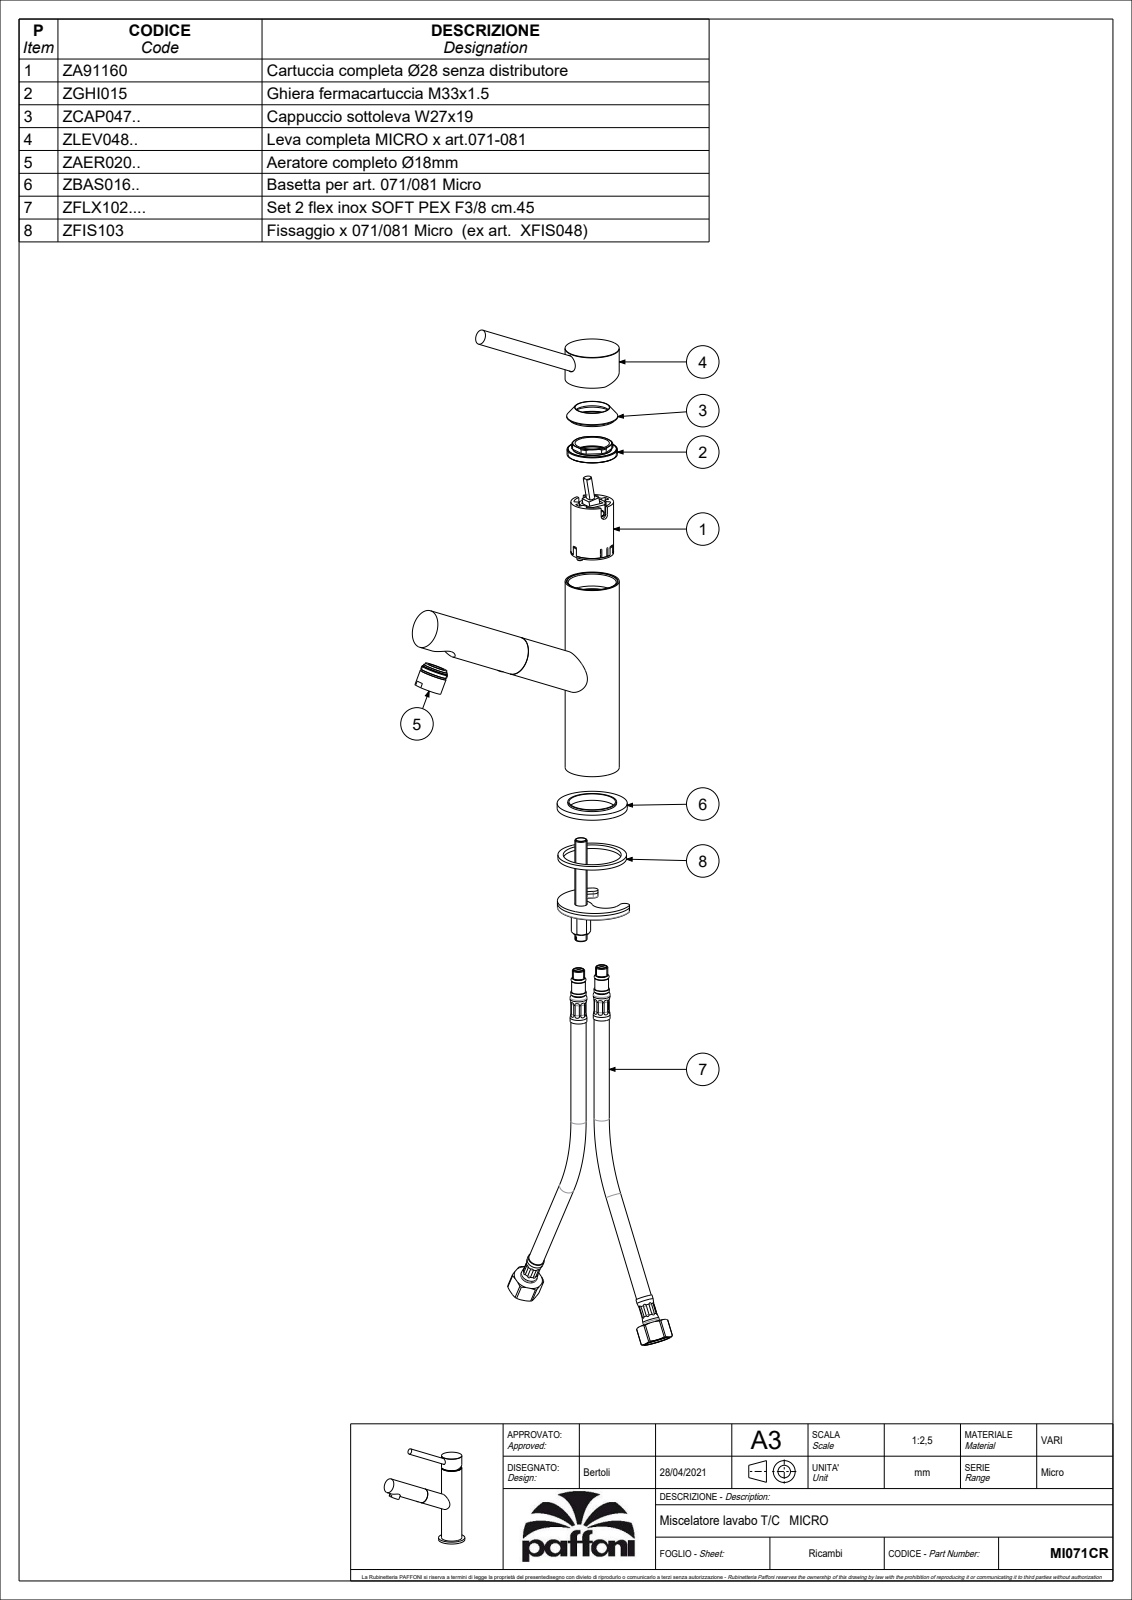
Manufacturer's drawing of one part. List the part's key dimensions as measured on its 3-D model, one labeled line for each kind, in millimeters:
Part name (STEP PRODUCT): MI071CR
STEP written by: CREO PARAMETRIC BY PTC INC, 2020044 (CONFIG_CONTROL_DESIGN)
Units: millimetres
Bodies: 1 solid, 578 faces (204 planar, 228 cylindrical, 146 other)
Overall size (bounding box): 187.04 × 162.1 × 46
Volume: 170 301 mm³ · Surface area: 67 702 mm²
Round holes (diameter × count): ⌀6 ×5, ⌀7 ×5, ⌀5.5 ×2, ⌀8.6 ×2, ⌀9.4 ×2, ⌀11 ×2, ⌀18.4 ×2, ⌀3.5 ×1, ⌀4.5 ×1, ⌀5.6 ×1, ⌀6.5 ×1, ⌀7.5 ×1
Round bosses / shafts (diameter × count): ⌀18 ×3, ⌀35.5 ×2, ⌀25 ×2, ⌀14 ×2, ⌀4 ×2, ⌀46 ×1, ⌀37 ×1, ⌀33.5 ×1
Partial cylindrical surfaces — rounded edges, fillets, slot ends (radius × count): R0.3 ×18, R0.5 ×12, R2.5 ×2, R1.05 ×1, R2.15 ×1, R2.75 ×1, R8 ×1, R12 ×1
Main face-to-face distances: 3.5, 10, 141.3, 13.5, 2, 3, 4.5, 131.3, 144.8, 2.5
Hole centre spacings: 6.87, 7.07, 7.11, 8.14, 8.44, 8.46, 8.54, 10.12
